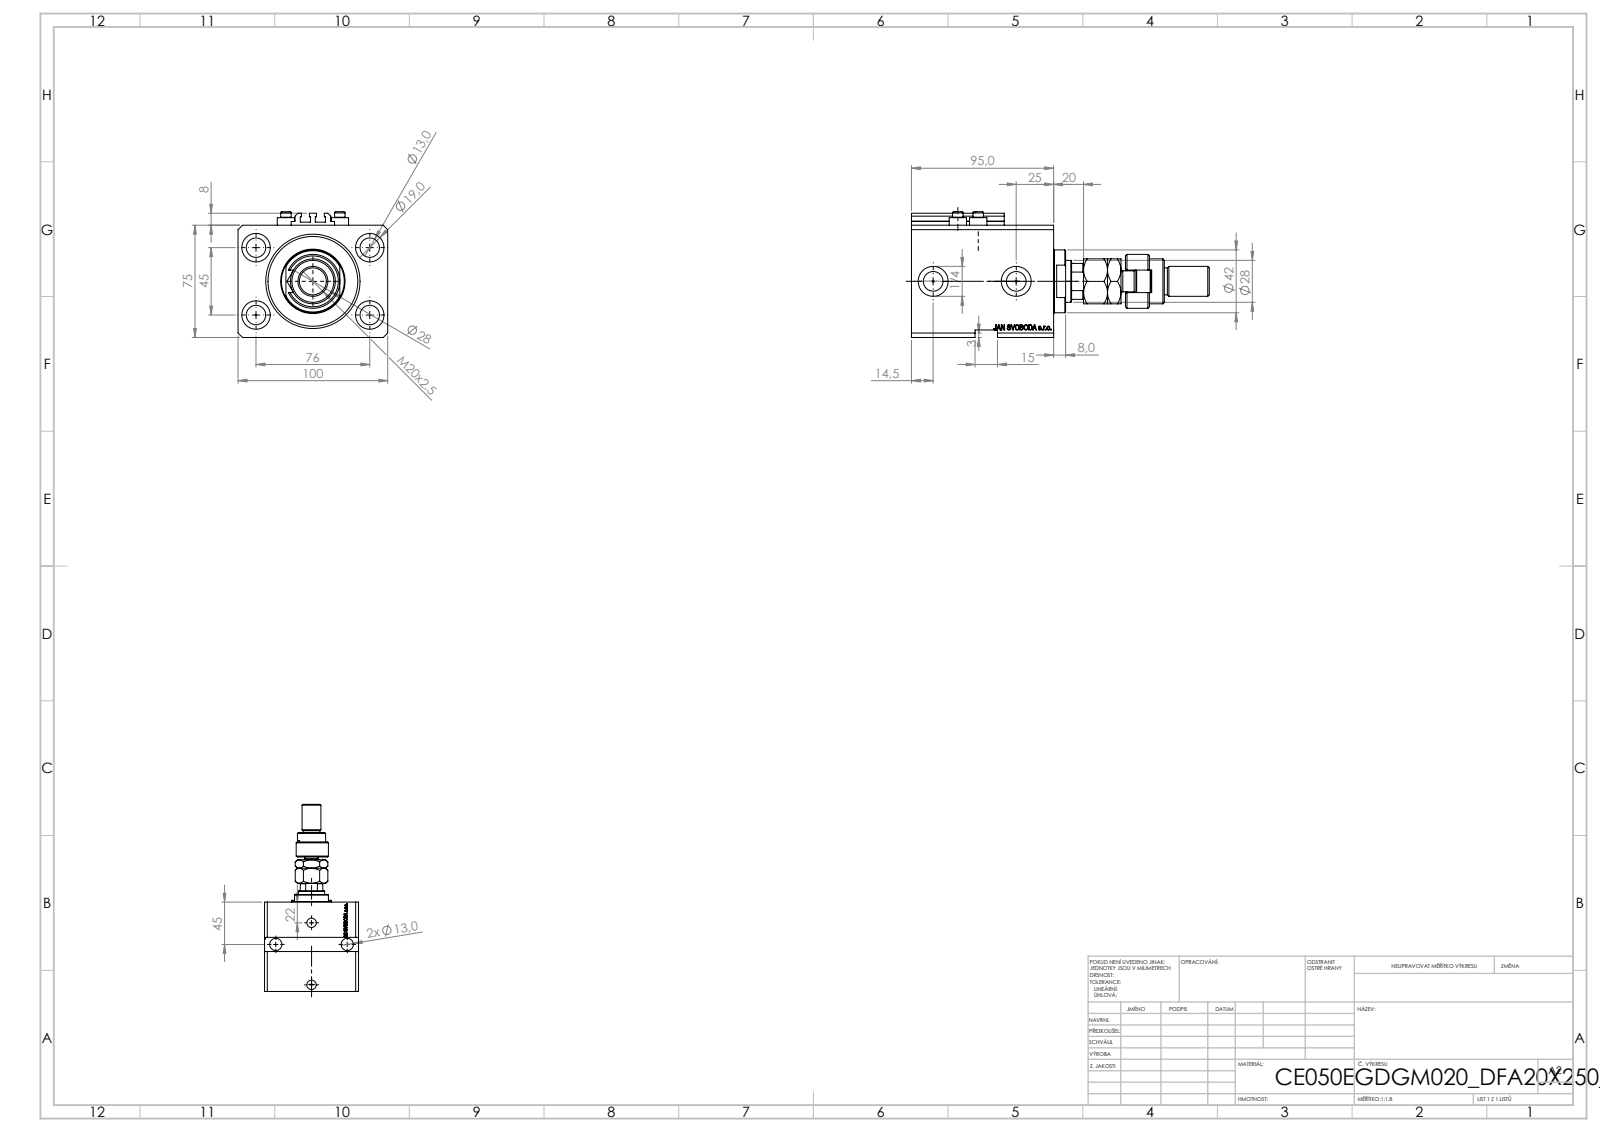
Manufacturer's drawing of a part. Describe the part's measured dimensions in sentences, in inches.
The part is named "V250CE_C_VCP; ALLEN BOLT V250CE; V250CE_E_Body; V250CE_VC_E (+2 more)". Its 3-D file was written by "SolidWorks 2019 (CONFIG_CONTROL_DESIGN)". It is 10 solids with 1189 faces: 567 planar, 151 cylindrical and 471 other. Overall it measures 7.831 by 3.937 by 3.307 inches. Its volume is 40.05 cubic inches and its surface area 213.8 square inches. Round holes: 6 of diameter 0.512, 4 of diameter 0.049, 4 of diameter 0.157, 4 of diameter 0.748, 2 of diameter 0.394, 2 of diameter 0.518, 2 of diameter 0.787, 1 of diameter 0.728, 1 of diameter 1.102, 1 of diameter 1.969, 1 of diameter 2.48. Round bosses or shafts: 4 of diameter 0.457, 4 of diameter 0.276, 1 of diameter 1.654, 1 of diameter 1.417, 1 of diameter 1.181, 1 of diameter 0.866, 1 of diameter 0.787, 1 of diameter 0.709. Partial cylindrical surfaces (rounded edges, fillets, slot ends): 10 of radius 0.008, 1 of radius 0.295, 1 of radius 0.472, 1 of radius 0.531. The main face-to-face distances are 2.953, 3.937, 3.74, 0.469, 3.272, 2.693, 2.224, 1.047, 1.181, 0.787. The hole center spacings are 1.739, 2.992, 0.535, 0.816, 1.086, 1.165, 1.181, 1.324.
